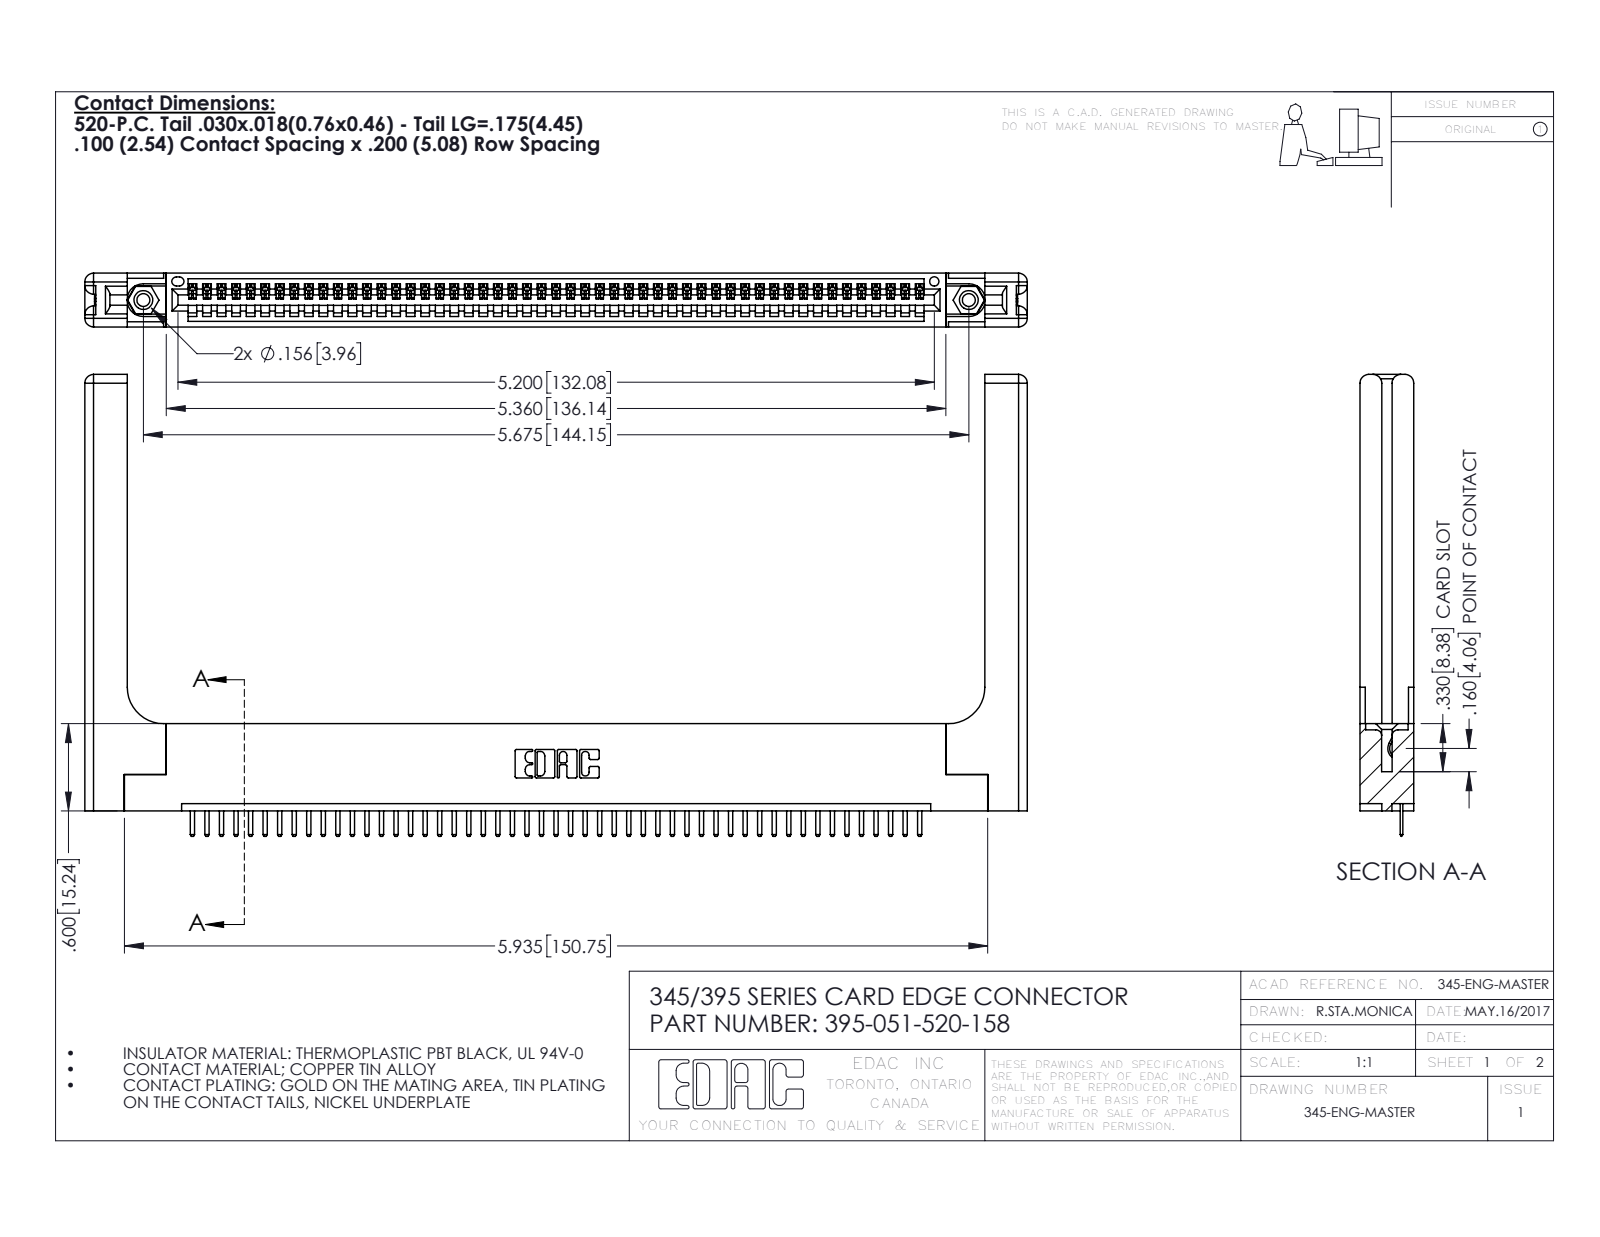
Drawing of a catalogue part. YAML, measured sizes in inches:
part_name: "345-220-058_345-220-058; 345-250-001_345-250-001-102; 345-292-001_345-293-120; 345 Part_Flush Mounting Lugs - 0.156 Dia-TH (+1 more)"
step_written_by: "SolidWorks 2016 (CONFIG_CONTROL_DESIGN)"
units: inches
bodies: {solids: 56, faces: 3544, planar: 2370, cylindrical: 1114, other: 60}
overall_size: [6.479, 3.175, 0.37]
volume: 1.468
surface_area: 39.72
round_holes:
  - {diameter: 0.089, count: 2}
  - {diameter: 0.125, count: 2}
  - {diameter: 0.156, count: 2}
  - {diameter: 0.064, count: 1}
round_bosses_or_shafts:
  - {diameter: 0.155, count: 2}
partial_cylinders:
  - {radius: 0.01, count: 104}
  - {radius: 0.006, count: 102}
  - {radius: 0.01, count: 22}
  - {radius: 0.06, count: 16}
  - {radius: 0.007, count: 6}
  - {radius: 0.031, count: 6}
  - {radius: 0.026, count: 3}
  - {radius: 0.03, count: 2}
face_to_face_distances: [0.37, 0.072, 0.298, 0.2, 0.098, 0.272, 0.025, 0.225, 0.148, 0.15]
hole_center_spacings: [0.27, 5.439, 5.675]
